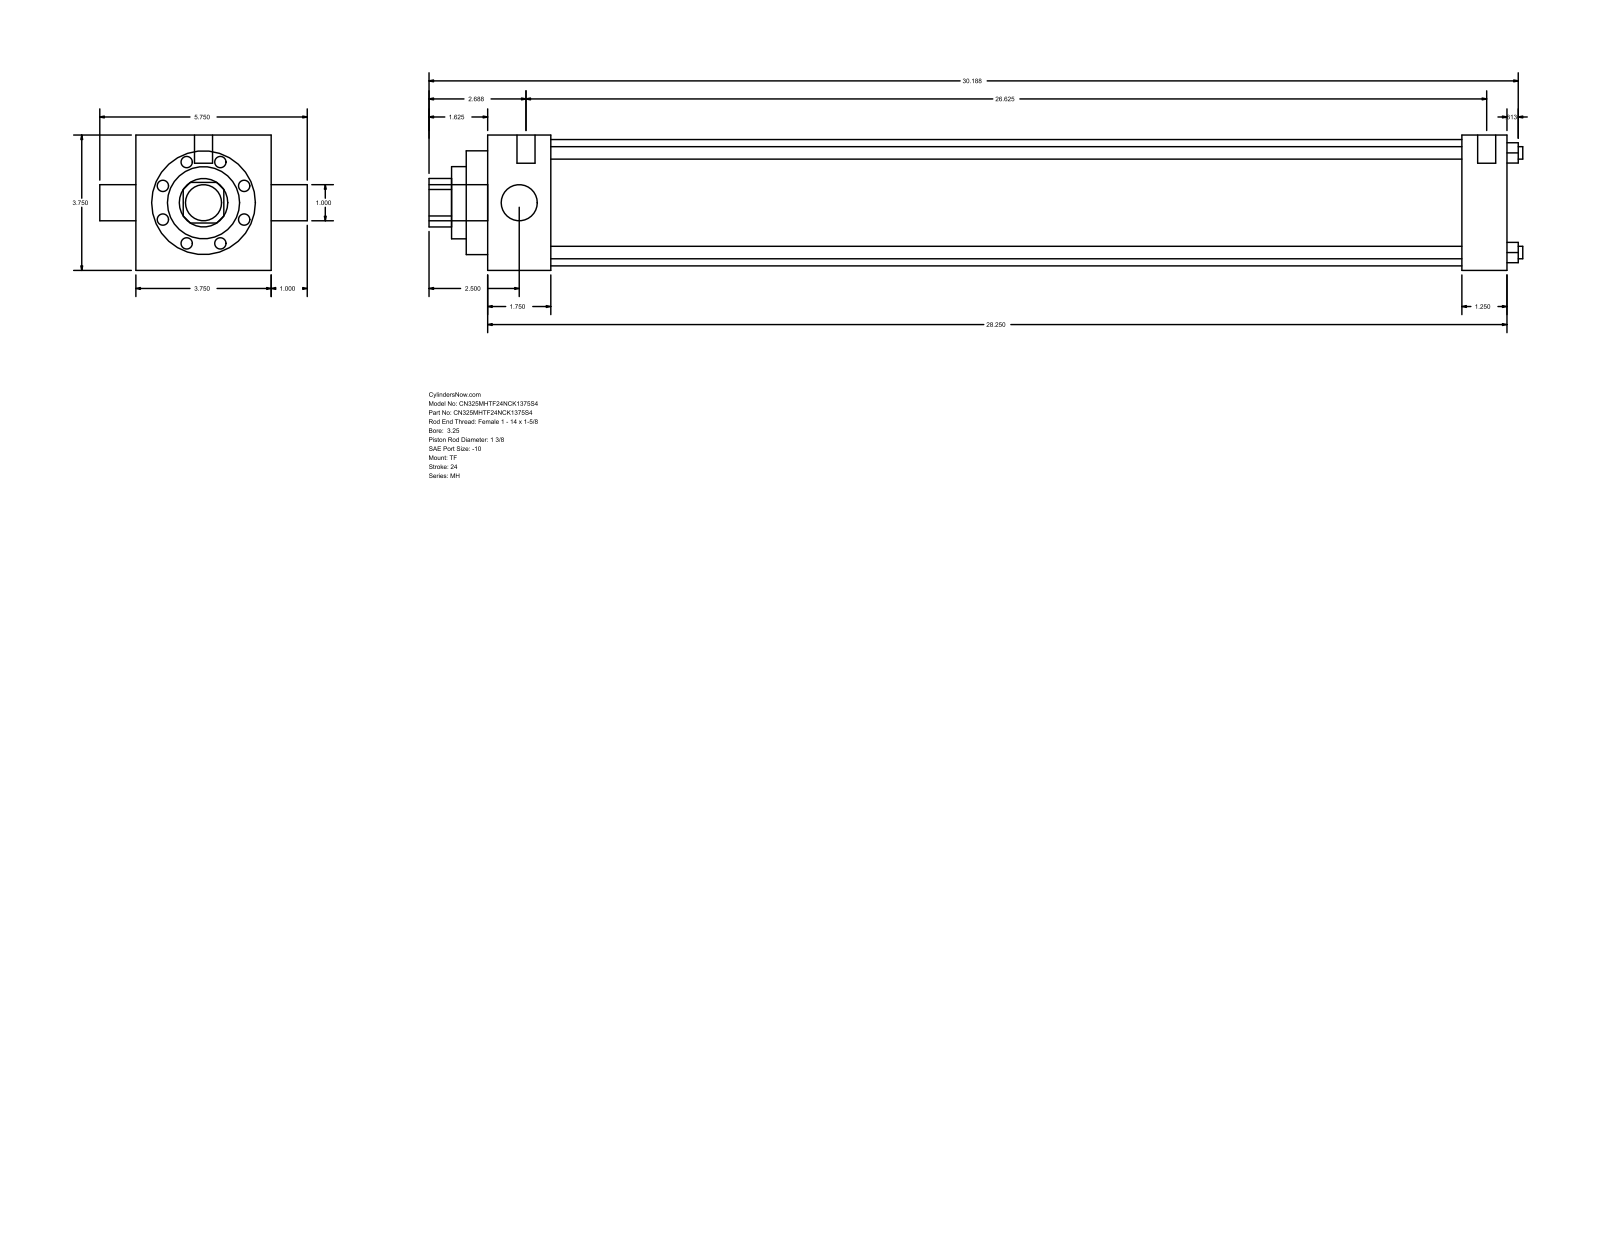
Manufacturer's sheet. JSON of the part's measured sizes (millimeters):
{"part_name": "MH_TF__0325_1.375", "step_written_by": "GSSL Pune (CONFIG_CONTROL_DESIGN)", "units": "millimeters", "bodies": {"solids": 0, "faces": 86, "planar": 61, "cylindrical": 25, "other": 0}, "overall_size": [769.94, 146.05, 95.25], "round_holes": [[8.76, 4], [25.4, 1], [34.92, 1], [50.8, 1], [73.03, 1], [88.9, 1]], "round_bosses_or_shafts": [[5.56, 3], [12.7, 2], [25.4, 1]], "partial_cylinders_radius": [[17.06, 1]], "face_to_face_distances": [95.24, 717.56, 44.45, 685.81, 641.36, 673.11, 31.75, 15.08, 59.53, 700.89], "hole_center_spacings": [49.57, 70.1, 99.14]}
